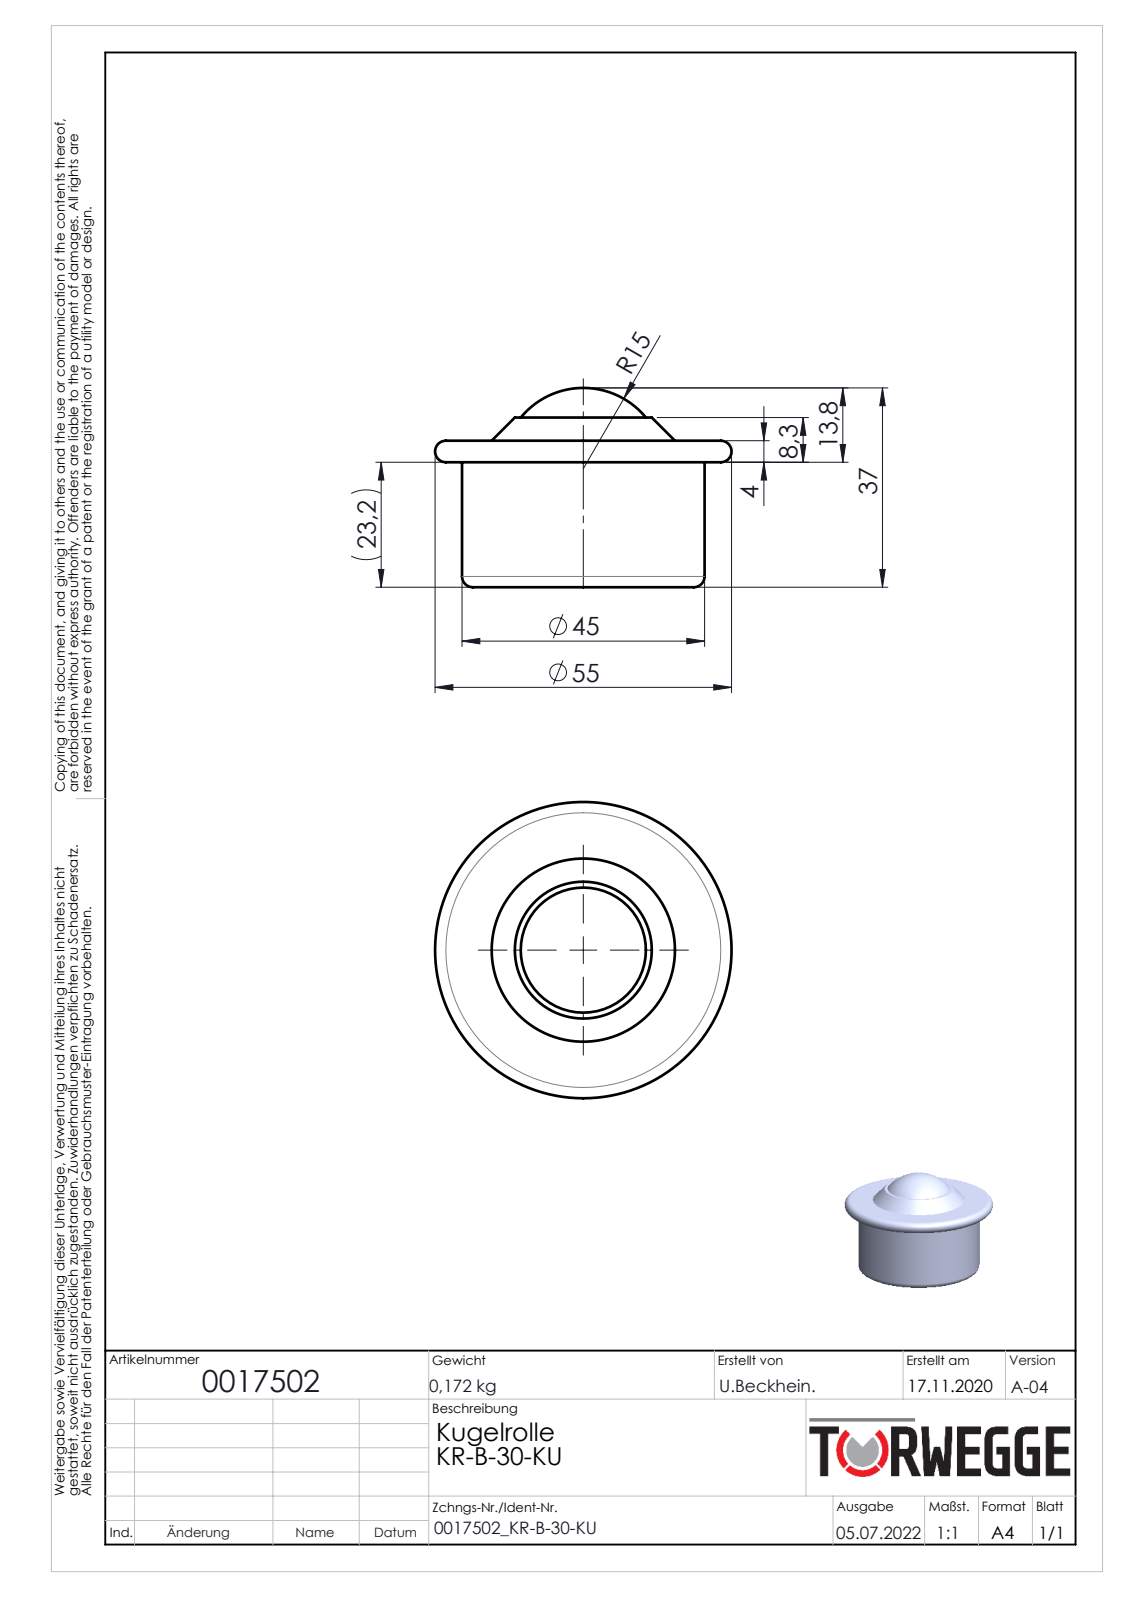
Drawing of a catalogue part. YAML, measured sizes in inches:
part_name: "0017502"
step_written_by: "SolidWorks 2020 (AUTOMOTIVE_DESIGN)"
units: inches
bodies: {solids: 1, faces: 15, planar: 4, cylindrical: 2, other: 9}
overall_size: [2.165, 2.165, 1.451]
volume: 3.066
surface_area: 13.27
round_bosses_or_shafts:
  - {diameter: 1.772, count: 1}
face_to_face_distances: [1.071, 0.913, 0.157, 1.24, 0.327, 0.169]
